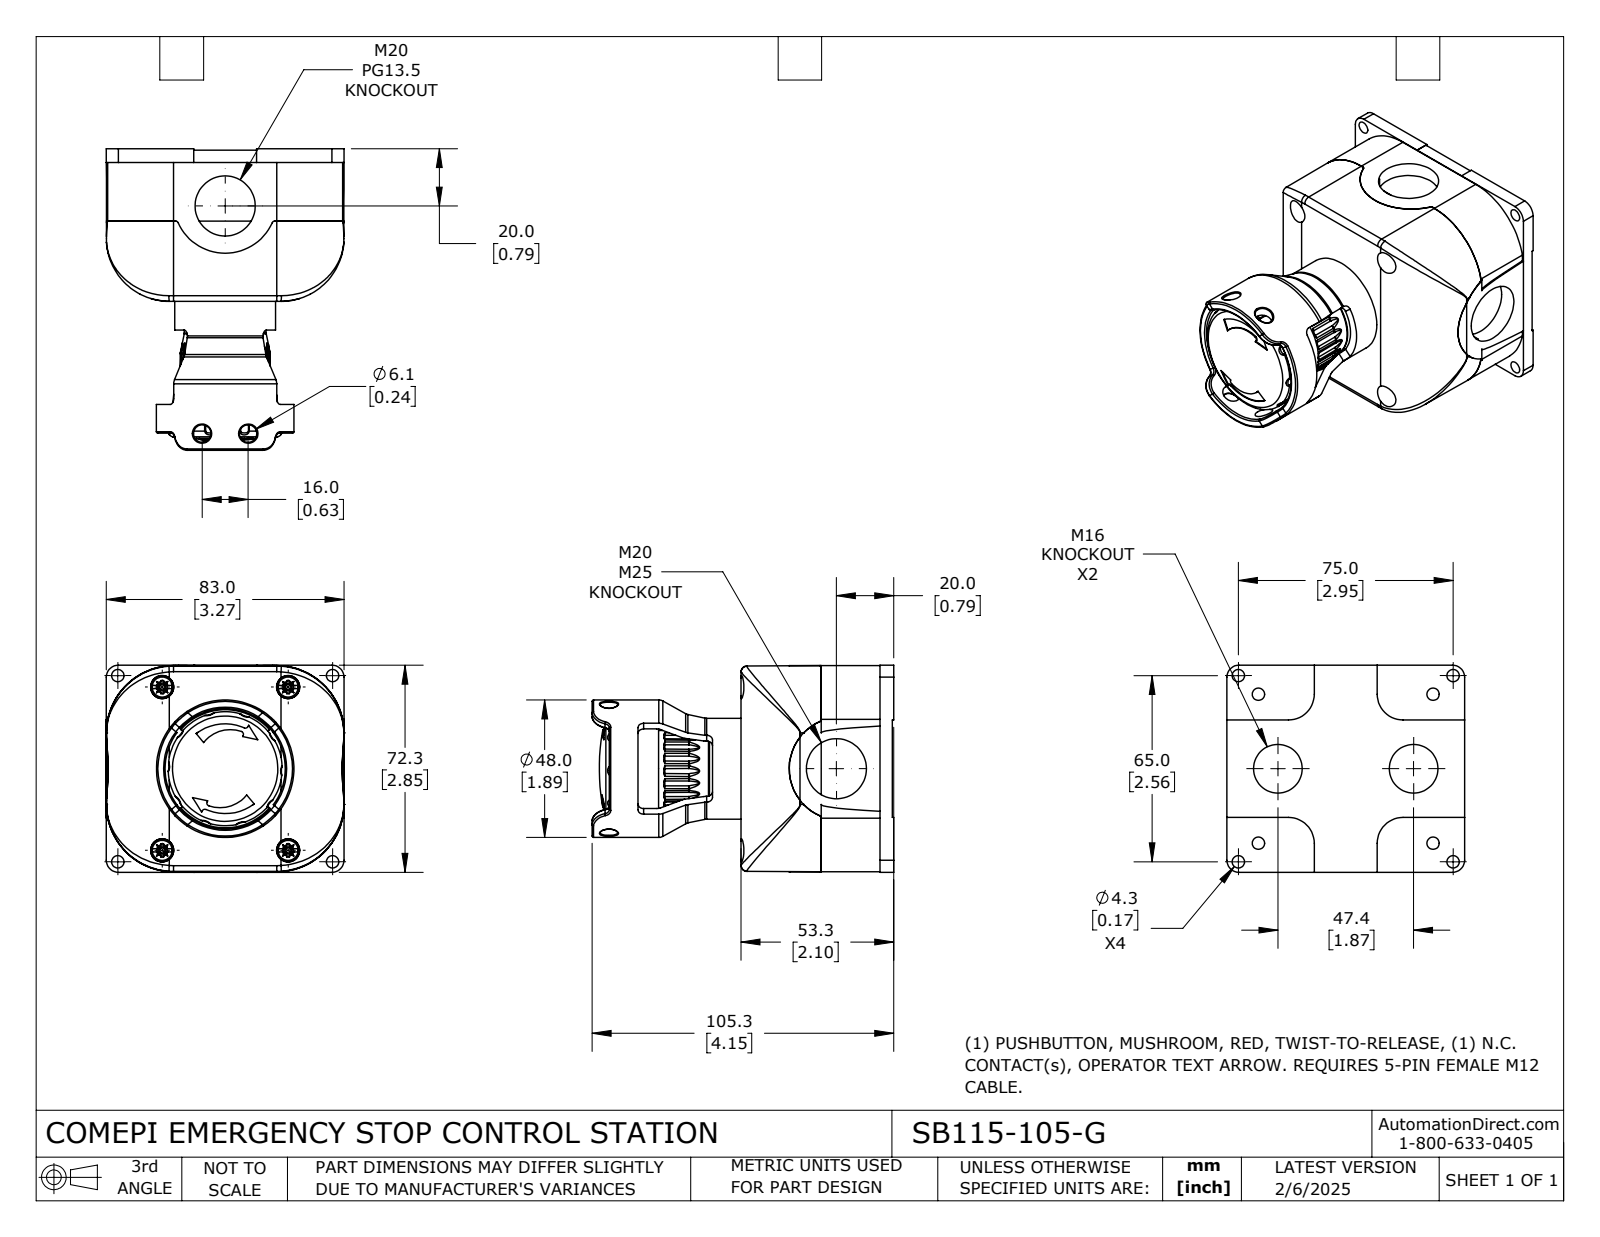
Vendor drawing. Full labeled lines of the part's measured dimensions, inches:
Part name (STEP PRODUCT): SB115-105-G
STEP written by: SolidWorks 2024 (CONFIG_CONTROL_DESIGN)
Units: inches
Bodies: 6 solids, 1015 faces (375 planar, 226 cylindrical, 414 other)
Overall size (bounding box): 4.146 × 3.268 × 2.846
Volume: 15.13 in³ · Surface area: 122.9 in²
Round holes (diameter × count): ⌀0.169 ×8, ⌀0.323 ×4, ⌀0.24 ×2, ⌀0.669 ×2, ⌀0.827 ×2, ⌀0.051 ×1, ⌀0.713 ×1, ⌀0.854 ×1, ⌀1.15 ×1, ⌀1.24 ×1, ⌀1.654 ×1
Round bosses / shafts (diameter × count): ⌀0.276 ×4, ⌀1.89 ×1, ⌀1.386 ×1, ⌀1.142 ×1, ⌀0.925 ×1, ⌀0.874 ×1, ⌀0.843 ×1
Partial cylindrical surfaces — rounded edges, fillets, slot ends (radius × count): R0.039 ×28, R0.079 ×16, R0.268 ×10, R0.035 ×4, R0.236 ×4, R0.354 ×4, R0.38 ×4, R0.925 ×4
Main face-to-face distances: 0.976, 0.098, 0.878, 2.079, 1.98, 1.102, 0.02, 0.118, 0.996, 2.098
Hole centre spacings: 0.376, 1.058, 1.39, 1.578, 1.954, 2.32, 2.367, 2.689
